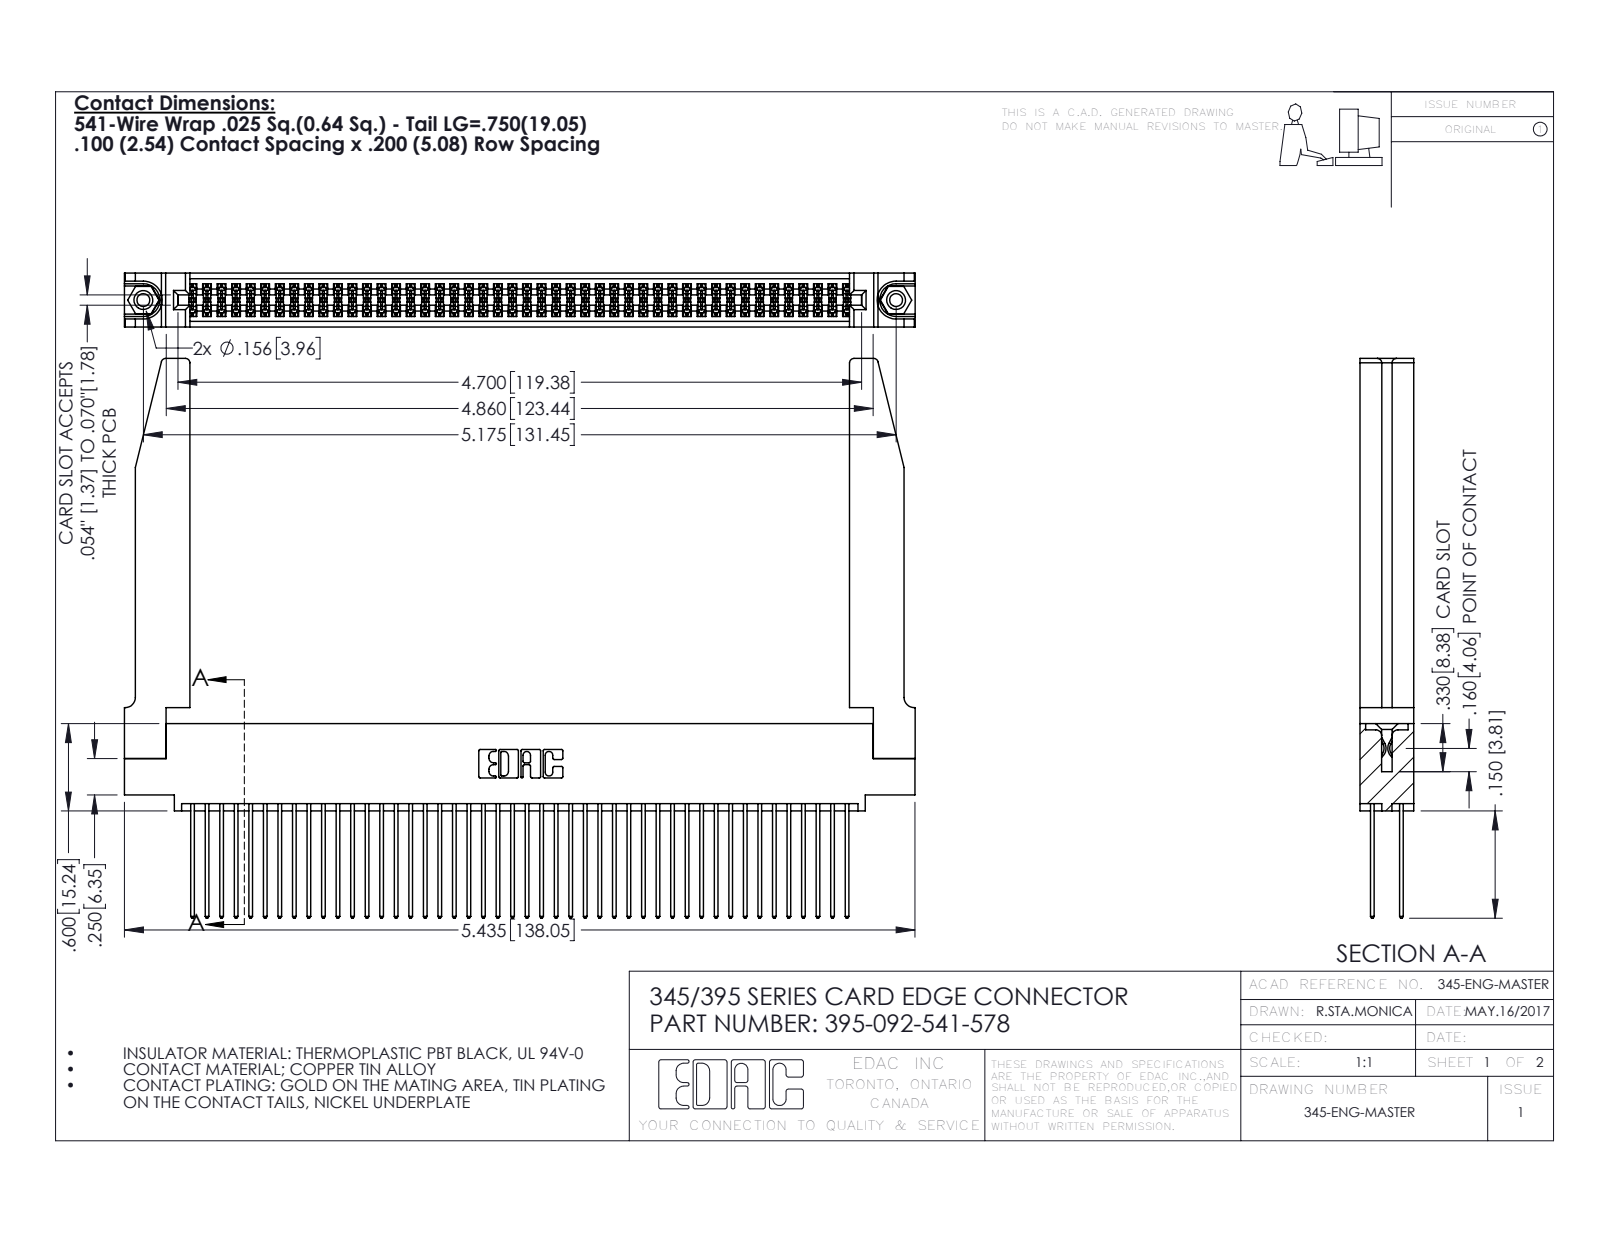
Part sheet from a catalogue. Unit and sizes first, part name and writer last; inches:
Units: inches
Overall size (bounding box): 5.436 × 3.847 × 0.37
Round holes (diameter × count): ⌀0.089 ×2, ⌀0.125 ×2, ⌀0.156 ×2, ⌀0.064 ×1
Round bosses / shafts (diameter × count): ⌀0.155 ×2
Partial cylindrical surfaces — rounded edges, fillets, slot ends (radius × count): R0.006 ×138, R0.01 ×92, R0.01 ×22, R0.03 ×8, R0.007 ×6, R0.031 ×6, R0.026 ×3, R0.014 ×2
Main face-to-face distances: 0.072, 0.298, 0.37, 0.2, 0.098, 0.272, 0.025, 0.225, 0.175, 0.148
Hole centre spacings: 0.27, 4.939, 5.175
Volume: 1.323 in³ · Surface area: 46.57 in²
Bodies: 97 solids, 4964 faces (3262 planar, 1650 cylindrical, 52 other)
Part name (STEP PRODUCT): 345-250-001_345-250-001-102; 345 Part_0.110 Offset - 0.156 Dia-TH; 345-220-078_345-220-078; 345-292-001_345-293-141 (+1 more)
STEP written by: SolidWorks 2016 (CONFIG_CONTROL_DESIGN)
